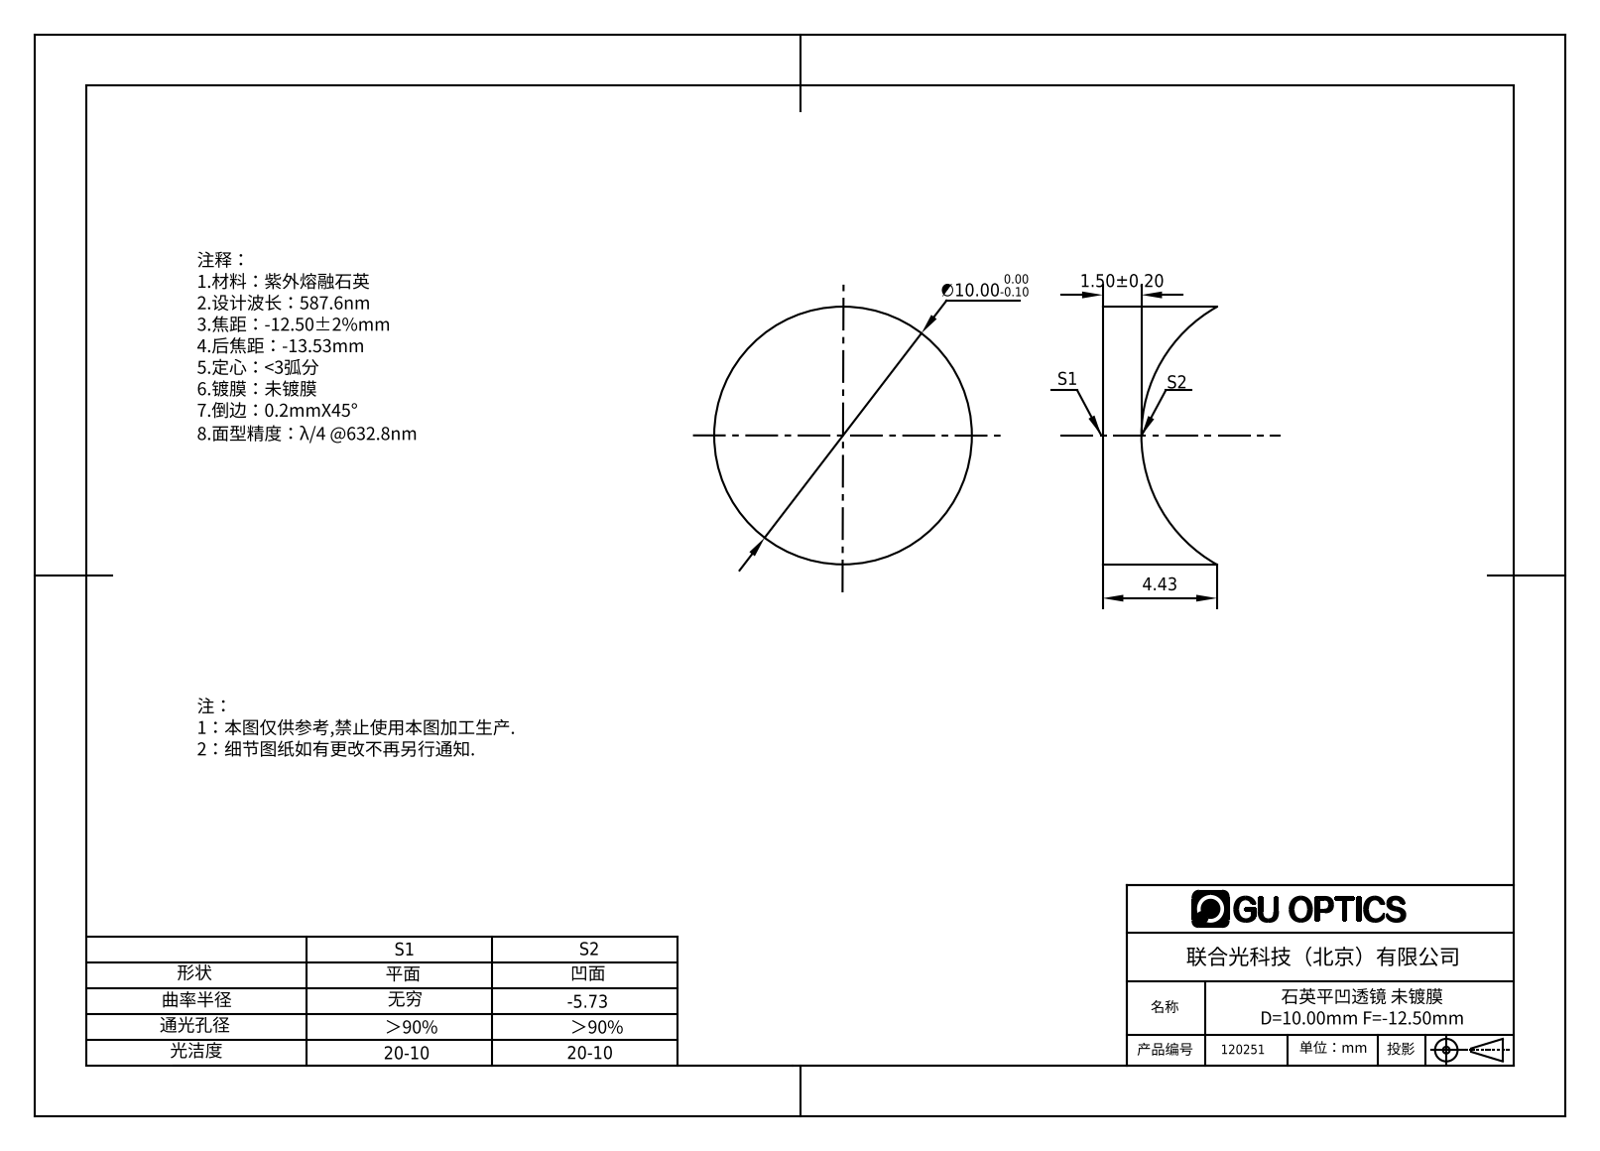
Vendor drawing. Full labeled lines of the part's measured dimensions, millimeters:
Part name (STEP PRODUCT): 120251
STEP written by: SolidWorks 2016 (AUTOMOTIVE_DESIGN)
Units: millimetres
Bodies: 1 solid, 5 faces (1 planar, 2 cylindrical, 2 other)
Overall size (bounding box): 10 × 10 × 4.43
Volume: 220 mm³ · Surface area: 323 mm²
Round bosses / shafts (diameter × count): ⌀10 ×1
